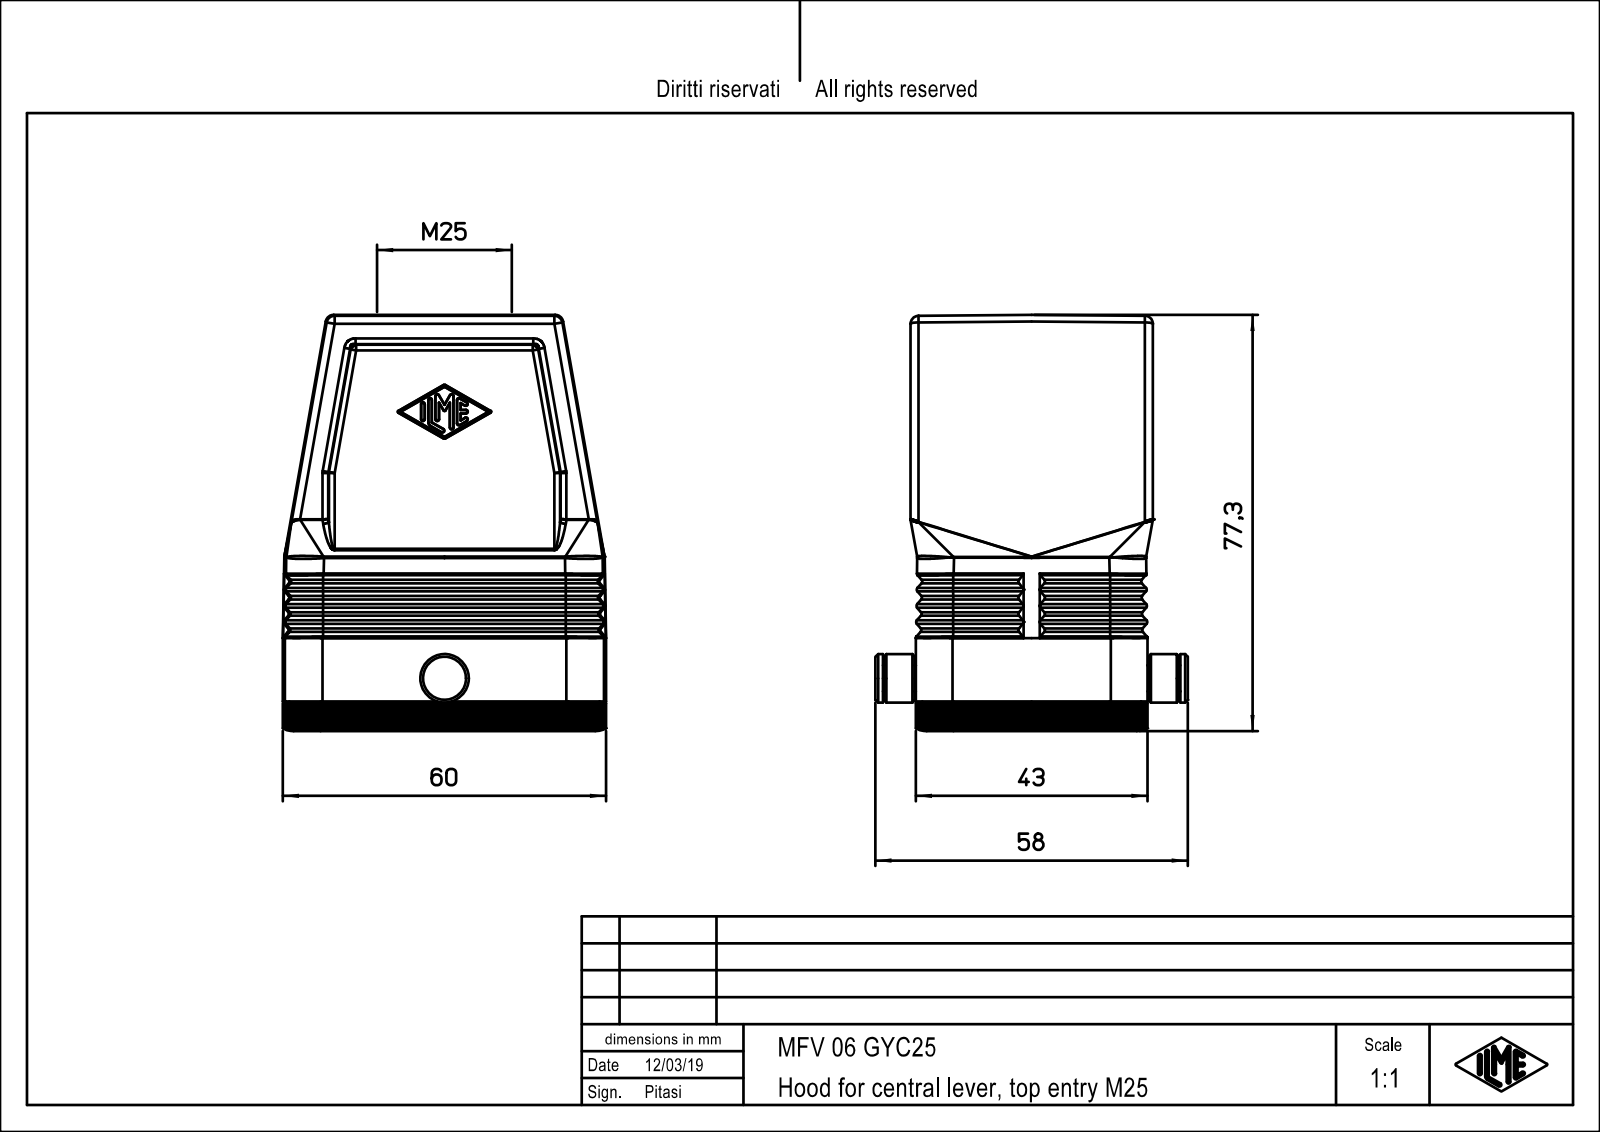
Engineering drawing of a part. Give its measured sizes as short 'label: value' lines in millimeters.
name: MFV_06_GYC25
written by: PTC Creo Elements/Direct Modeling 19.0E 27-Jun-2016 (C) Parametric Technology GmbH (AUTOMOTIVE_DESIGN)
unit: mm
bodies: 1 solid, 515 faces (169 planar, 168 cylindrical, 178 other)
size: 77.25 × 60 × 58
volume: 65 352 mm³; area: 32 196 mm²
holes: 4× ⌀3, 1× ⌀25
bosses: 1× ⌀9, 1× ⌀4.8
rounds: 54× R0.5, 44× R1.5, 12× R3, 12× R7, 4× R4, 4× R4.2, 4× R5.8
face distances: 43, 7, 4, 2, 7.55, 1, 44, 60, 39, 66.05
hole spacings: 25.81, 27, 44, 51.62
